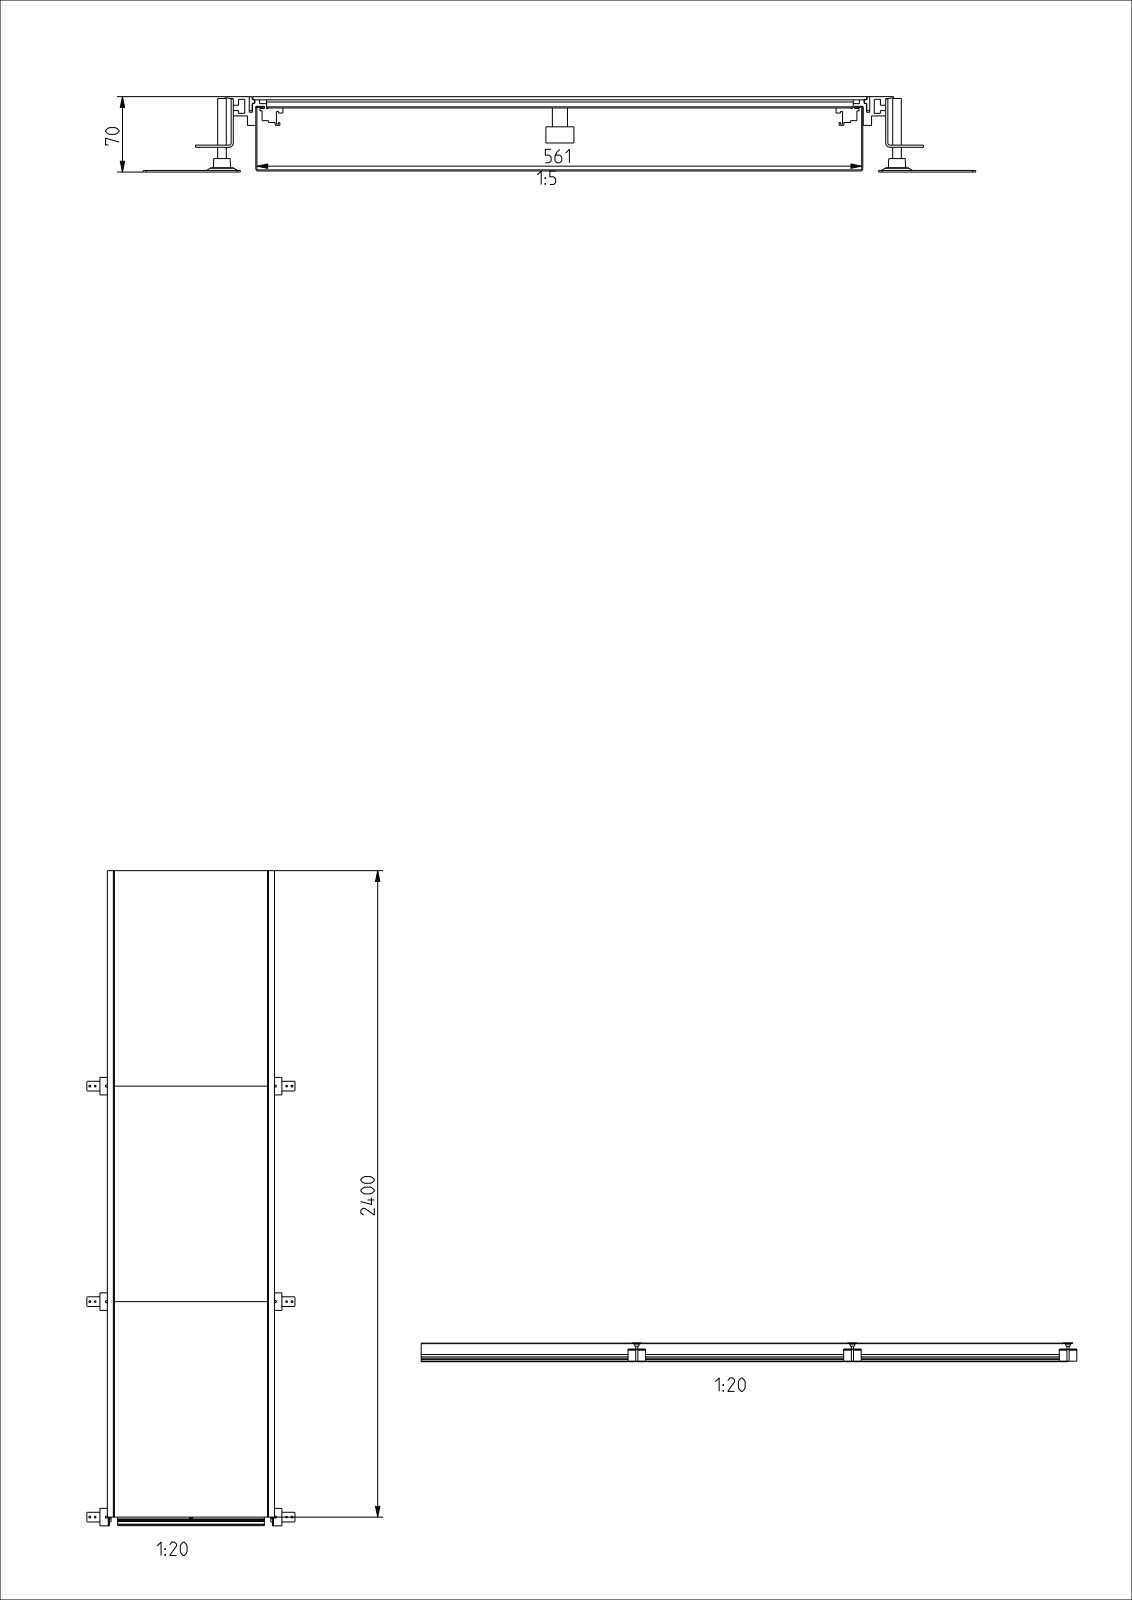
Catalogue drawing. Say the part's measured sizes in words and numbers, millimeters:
The part is named "U05644KUN; U05650KUN; U05647KUN; U05826KUN (+8 more)". Its 3-D file was written by "CREO PARAMETRIC BY PTC INC, 2020281 (AUTOMOTIVE_DESIGN)". It is 61 solids with 1036 faces: 606 planar, 358 cylindrical and 72 other. Overall it measures 2432.5 by 772.13 by 70 millimeters. Its volume is 10 310 000 cubic millimeters and its surface area 8 588 000 square millimeters. Round holes: 15 of diameter 7, 9 of diameter 8, 9 of diameter 10, 6 of diameter 6, 6 of diameter 8.5, 6 of diameter 11.5, 6 of diameter 17.5, 6 of diameter 23. Round bosses or shafts: 9 of diameter 26, 9 of diameter 14, 9 of diameter 11.9, 6 of diameter 20, 6 of diameter 8. Partial cylindrical surfaces (rounded edges, fillets, slot ends): 96 of radius 2, 24 of radius 3, 20 of radius 0.5, 4 of radius 1, 2 of radius 4. The main face-to-face distances are 1, 3, 65, 66, 69, 68, 7.5, 6.5, 562, 58.5. The hole center spacings are 800, 1600, 800.25, 801.1, 802.4, 1042.3, 1055.24, 1083.09.
